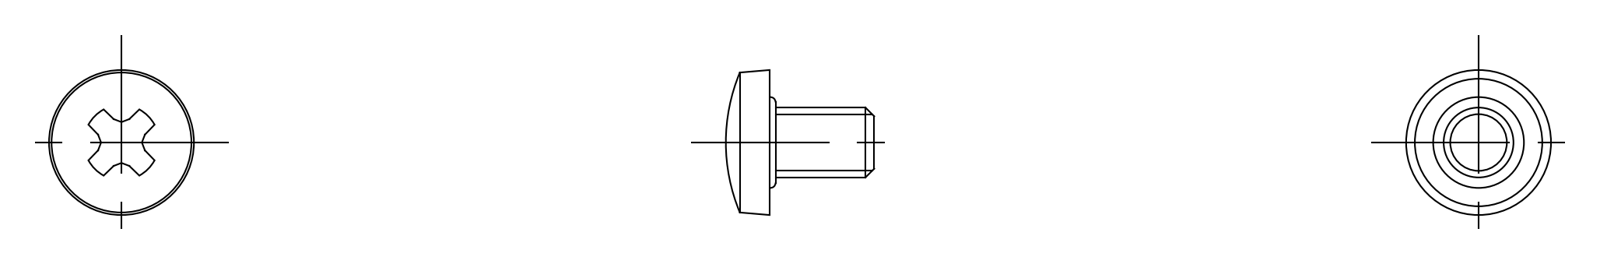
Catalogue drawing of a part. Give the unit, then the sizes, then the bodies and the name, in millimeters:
Units: millimetres
Overall size (bounding box): 8.44 × 8.3 × 8.3
Round holes (diameter × count): ⌀7.3 ×1
Round bosses / shafts (diameter × count): ⌀4 ×1
Partial cylindrical surfaces — rounded edges, fillets, slot ends (radius × count): R2.15 ×1
Main face-to-face distances: 1.25, 1.5, 7.5, 6.25, 6, 1.26, 2.18
Volume: 171 mm³ · Surface area: 270 mm²
Bodies: 2 solids, 38 faces (20 planar, 8 cylindrical, 10 other)
Part name (STEP PRODUCT): screw; TL_417_M4_6
STEP written by: SolidWorks 2015 (AUTOMOTIVE_DESIGN)
